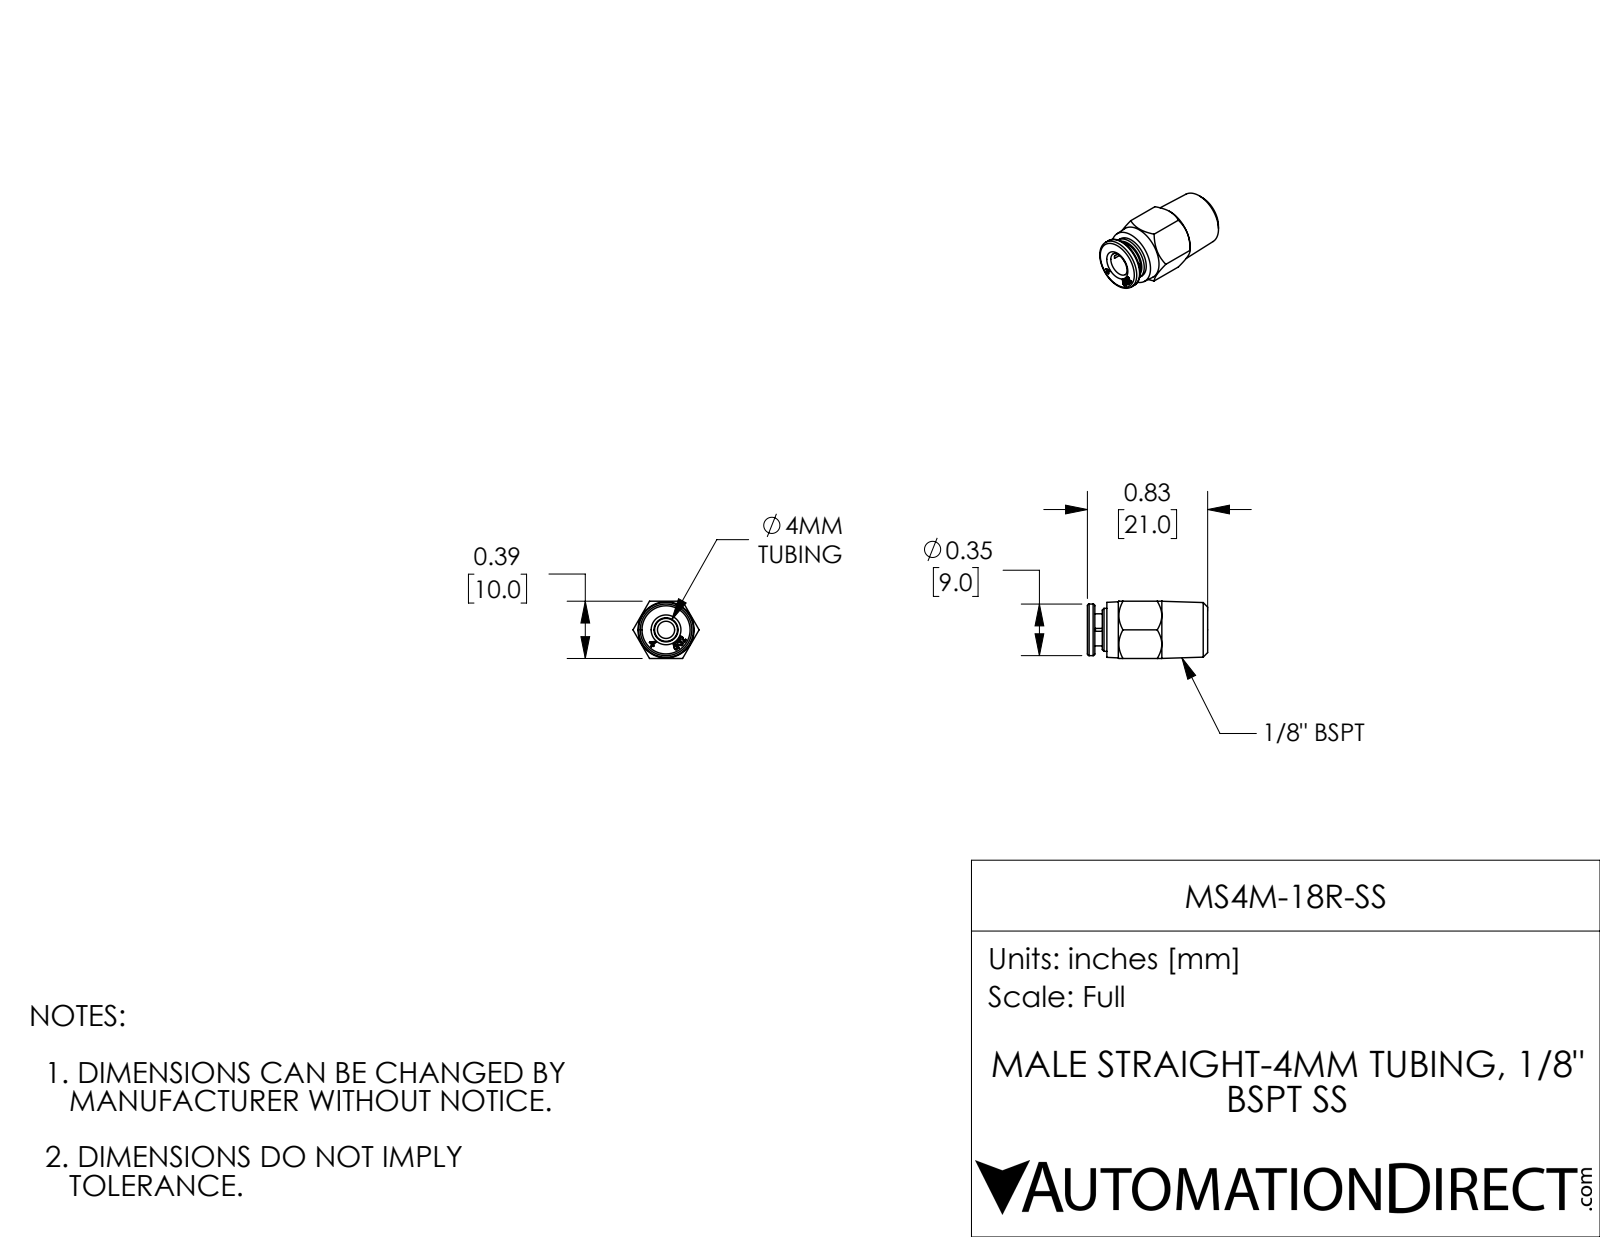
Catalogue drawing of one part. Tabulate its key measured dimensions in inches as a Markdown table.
| quantity | value |
| --- | --- |
| part name | MS4M-18R-SS |
| STEP written by | SolidWorks 2017 (AUTOMOTIVE_DESIGN) |
| units | inches |
| bodies | 1 solid, 131 faces (57 planar, 10 cylindrical, 64 other) |
| overall size | 0.827 × 0.455 × 0.394 |
| volume | 0.078 in³ |
| surface area | 1.732 in² |
| round holes (diameter × count) | 0.118 × 1, 0.165 × 1 |
| round bosses / shafts (diameter × count) | 0.354 × 1, 0.295 × 1, 0.22 × 1 |
| main face-to-face distances | 0.394, 0.051, 0.827, 0.776, 0.693, 0.083, 0.134, 0.031, 0.724, 0.102 |
